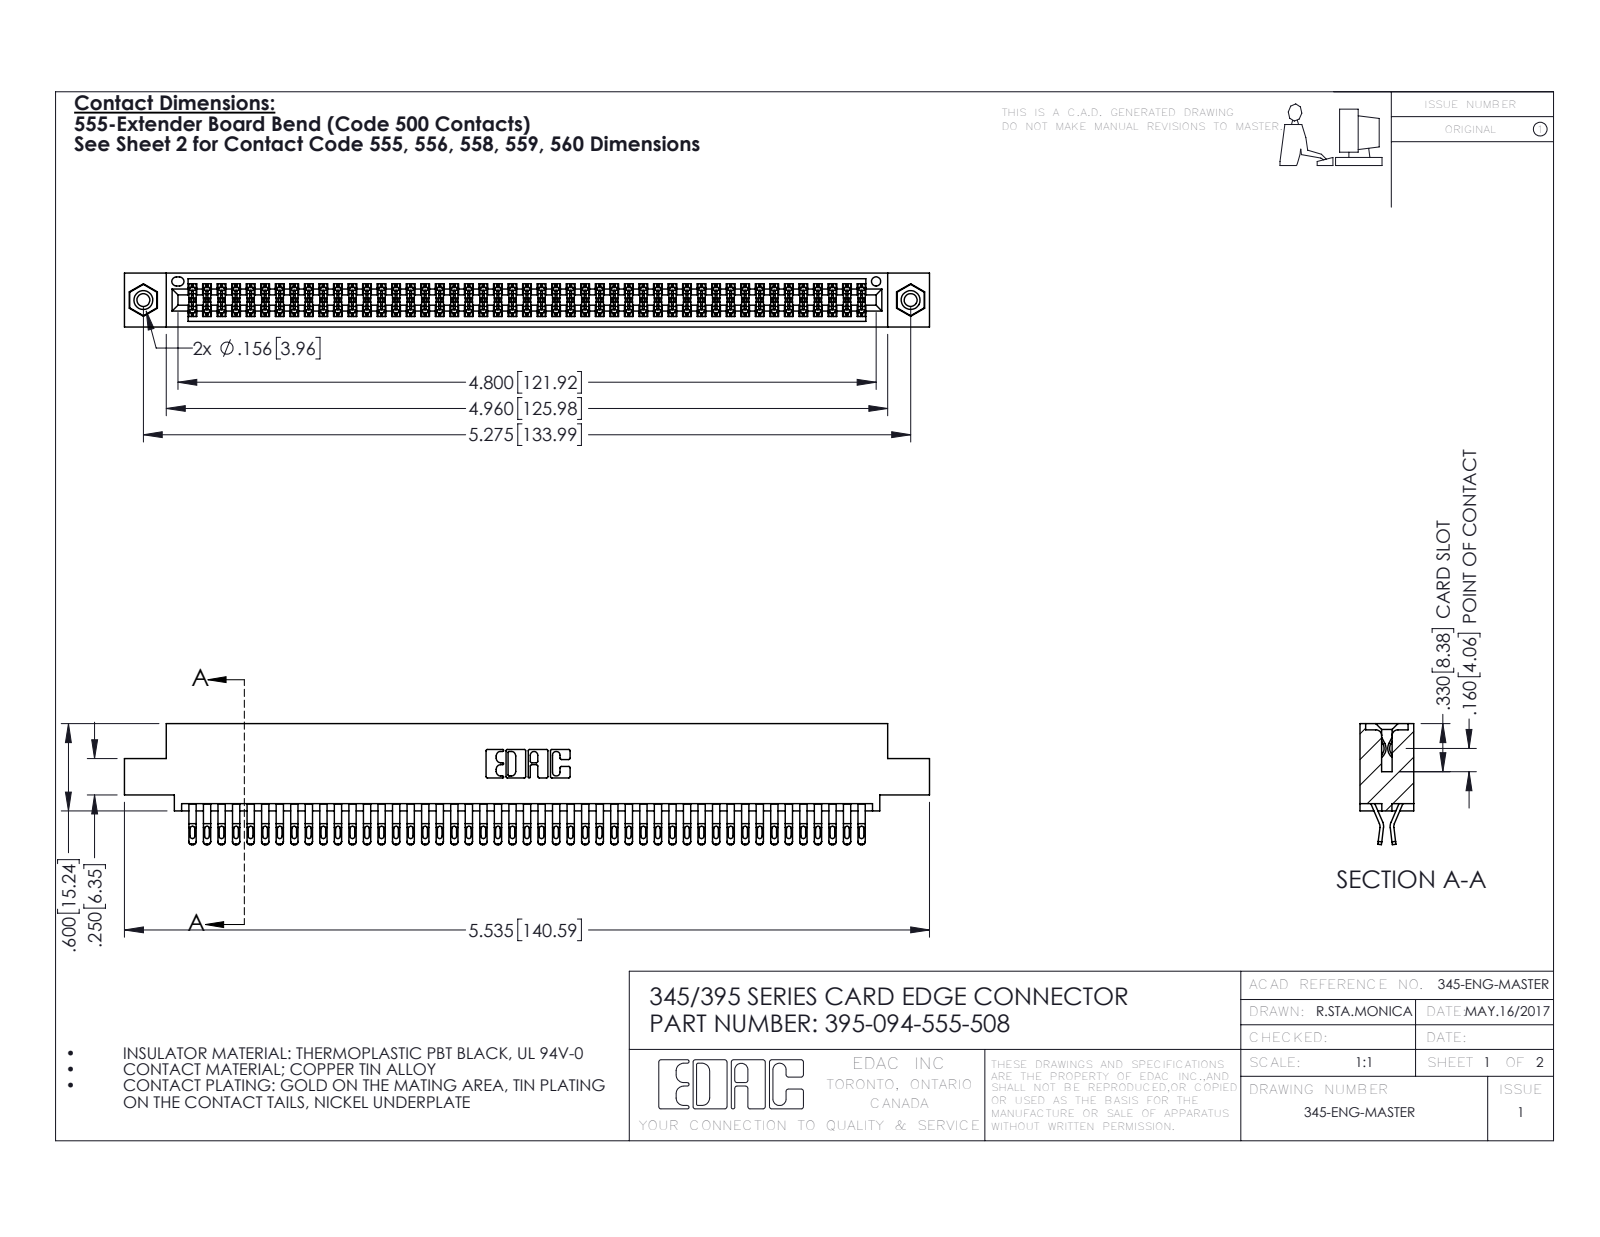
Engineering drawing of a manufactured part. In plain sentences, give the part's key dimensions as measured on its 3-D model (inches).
The part is named "345-292-001_555 Tail; 345-250-001_345-250-003-102; 395-094-555-508; 345 Part_0.110 Offset - 0.156 Dia-TI". Its 3-D file was written by "SolidWorks 2016 (CONFIG_CONTROL_DESIGN)". It is 97 solids with 5454 faces: 3030 planar, 2408 cylindrical and 16 other. Overall it measures 5.535 by 0.832 by 0.37 inches. Its volume is 0.848 cubic inches and its surface area 33.62 square inches. Round holes: 2 of diameter 0.089, 2 of diameter 0.125, 2 of diameter 0.156, 1 of diameter 0.064. Round bosses or shafts: 2 of diameter 0.155. Partial cylindrical surfaces (rounded edges, fillets, slot ends): 235 of radius 0.016, 188 of radius 0.02, 141 of radius 0.006, 22 of radius 0.01, 6 of radius 0.007, 6 of radius 0.031, 3 of radius 0.026, 2 of radius 0.01. The main face-to-face distances are 0.072, 0.298, 0.025, 0.37, 0.2, 0.098, 0.272, 0.225, 0.175, 0.149. The hole center spacings are 0.27, 5.039, 5.275.
